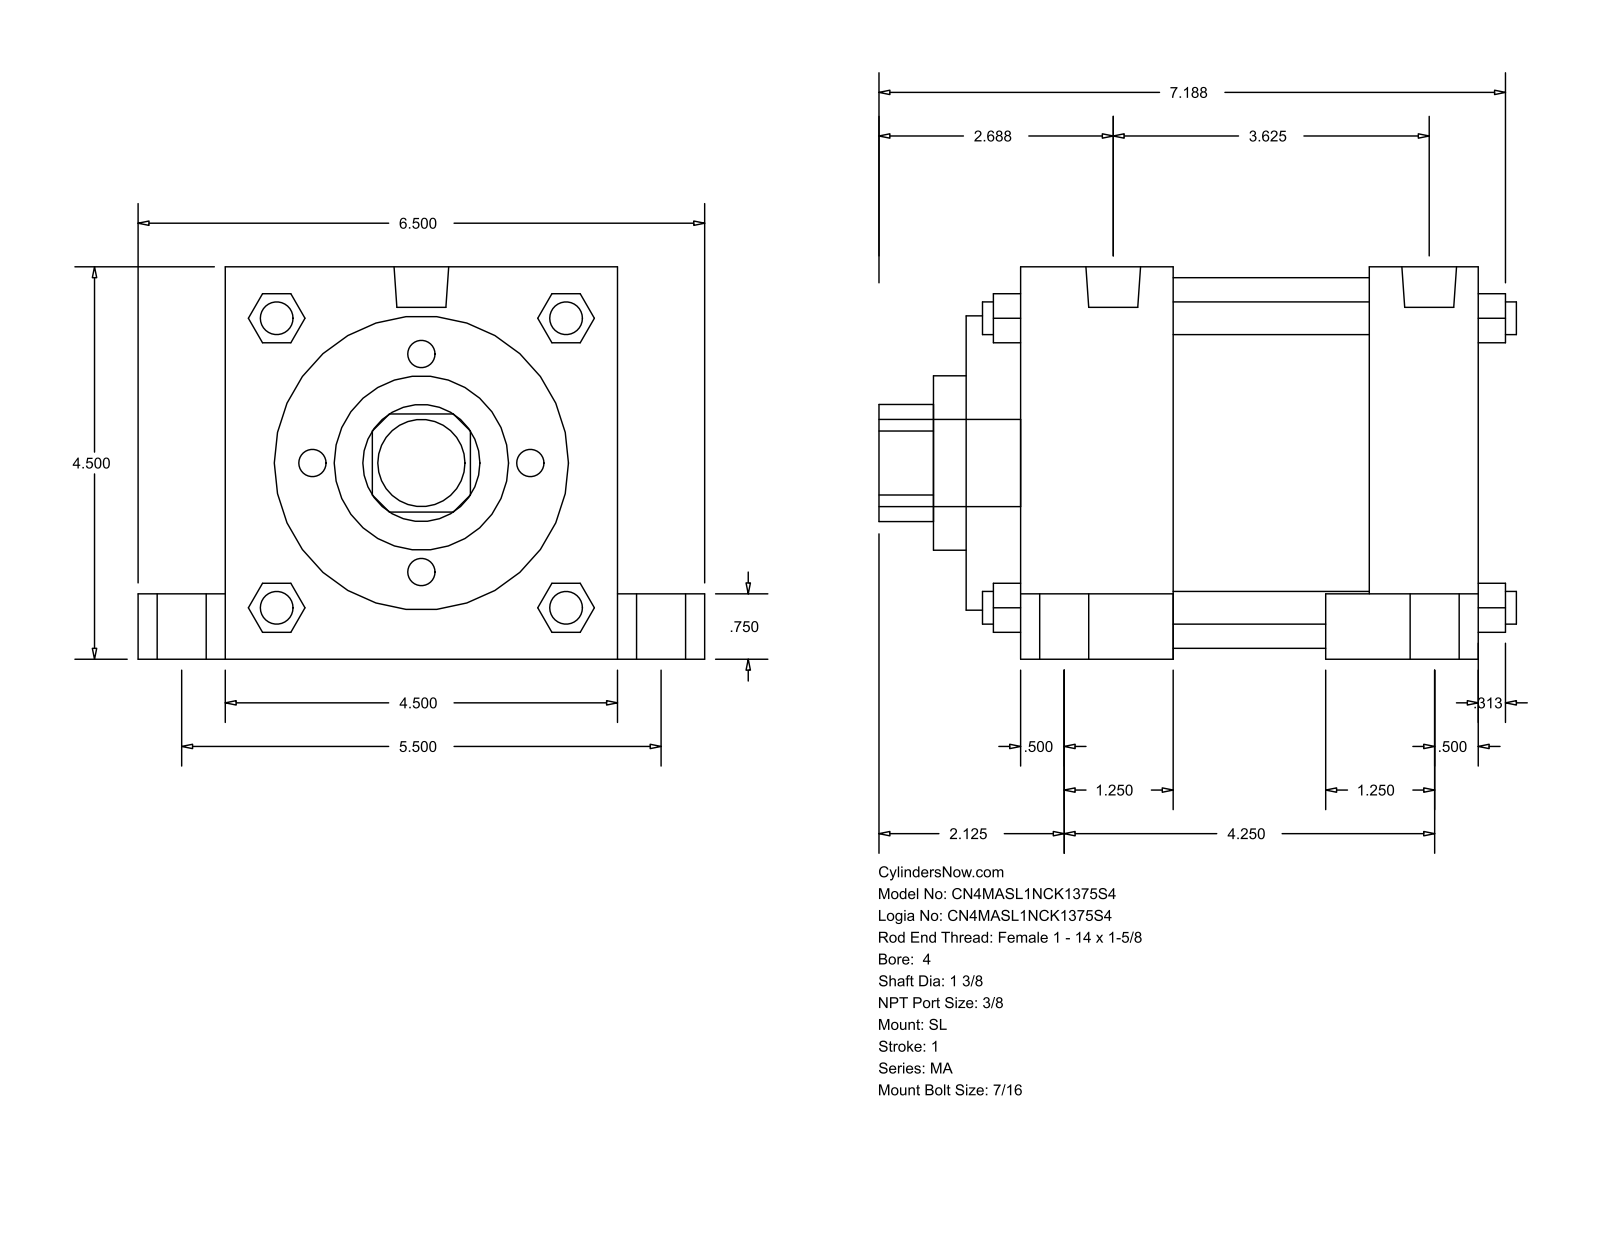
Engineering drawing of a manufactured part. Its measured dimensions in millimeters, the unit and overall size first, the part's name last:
Units: millimetres
Overall size (bounding box): 185.74 × 165.1 × 114.3
Round holes (diameter × count): ⌀34.92 ×1, ⌀50.8 ×1, ⌀85.72 ×1, ⌀107.95 ×1
Round bosses / shafts (diameter × count): ⌀20.64 ×4, ⌀14.29 ×4, ⌀11.11 ×4, ⌀9.53 ×4, ⌀15.93 ×2, ⌀25.4 ×1
Partial cylindrical surfaces — rounded edges, fillets, slot ends (radius × count): R17.06 ×1
Main face-to-face distances: 114.3, 133.35, 149.22, 15.87, 60.32, 44.45, 88.9, 117.48, 101.61, 57.16
Bodies: 0 solids, 150 faces (113 planar, 37 cylindrical, 0 other)
Part name (STEP PRODUCT): MA_SL__0400_1.375
STEP written by: GSSL Pune (CONFIG_CONTROL_DESIGN)
